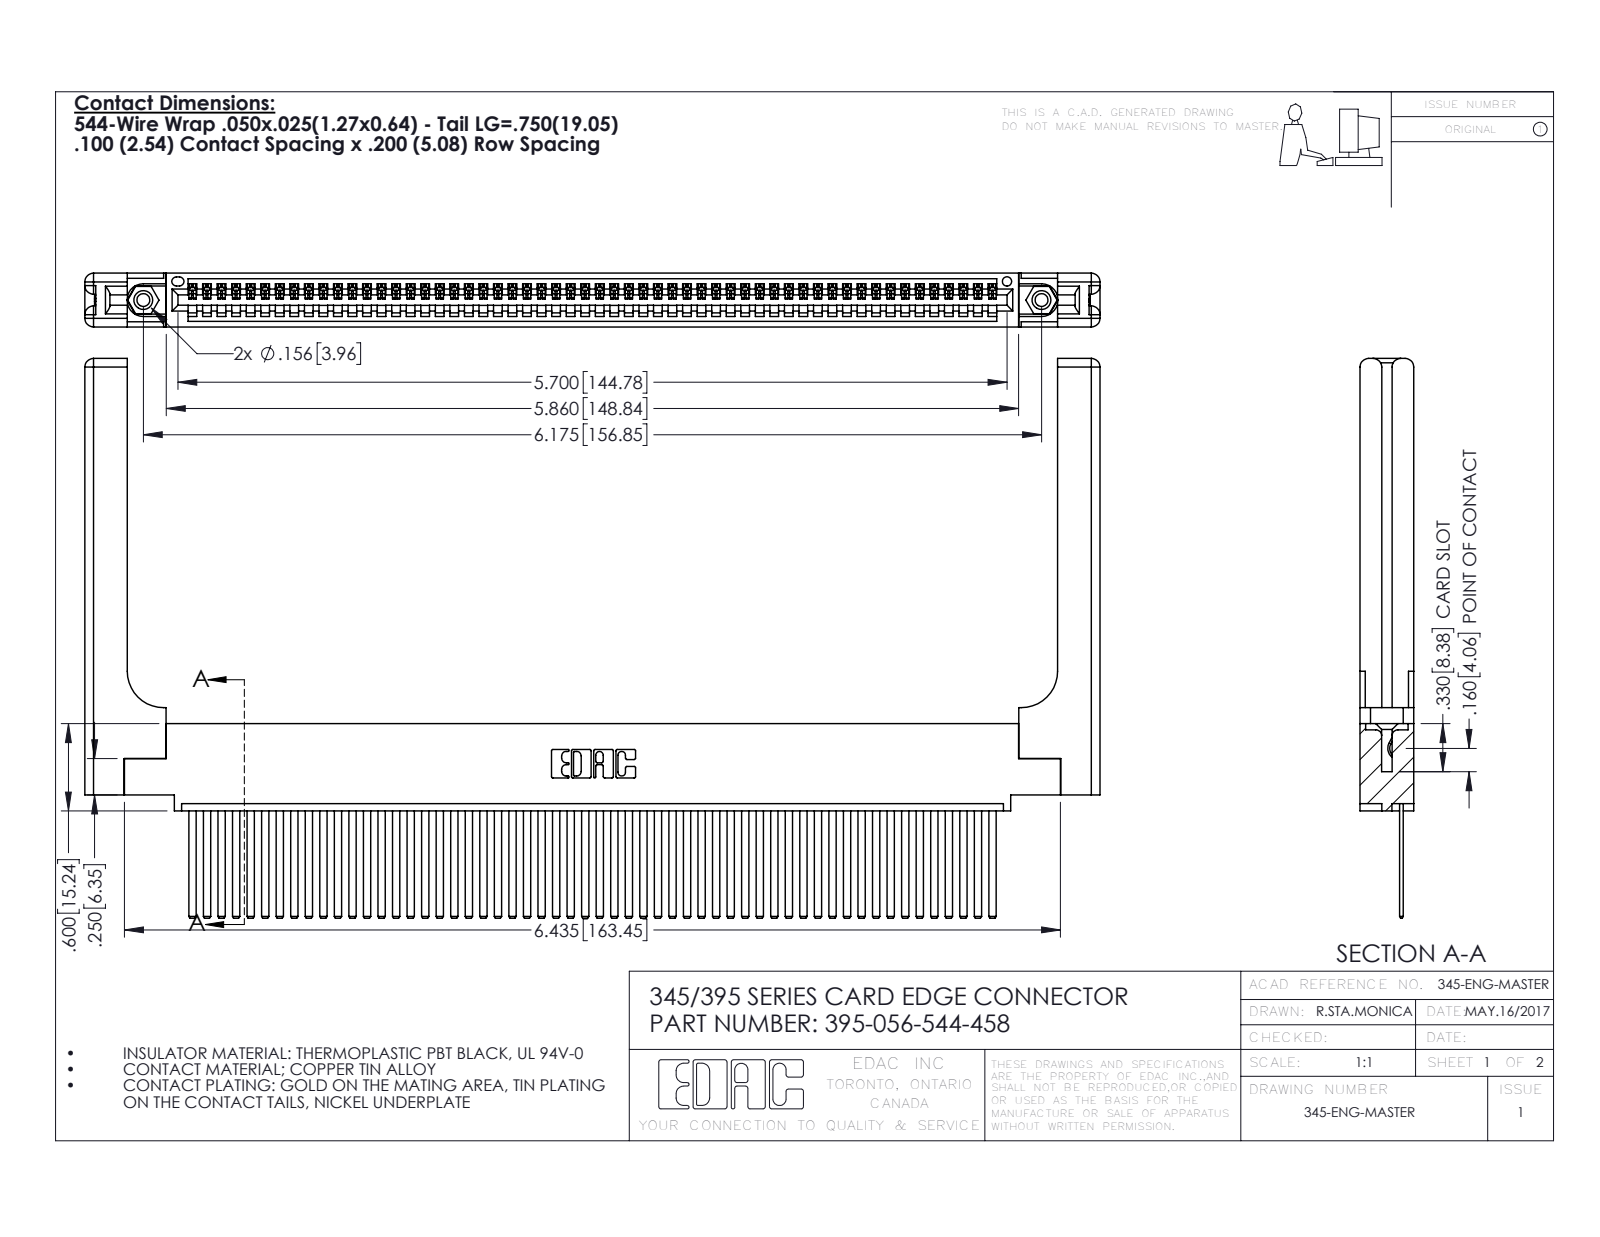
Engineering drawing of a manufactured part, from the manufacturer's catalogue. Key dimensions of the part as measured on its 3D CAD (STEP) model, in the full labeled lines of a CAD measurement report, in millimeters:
Part name (STEP PRODUCT): 345-292-001_345-293-144; 345 Part_0.110 Offset - 0.156 Dia-TH; 345-220-058_345-220-058; 395-056-544-458 (+1 more)
STEP written by: SolidWorks 2016 (CONFIG_CONTROL_DESIGN)
Units: millimetres
Bodies: 61 solids, 3298 faces (2248 planar, 990 cylindrical, 60 other)
Overall size (bounding box): 177.3 × 97.7 × 9.4
Volume: 26 040 mm³ · Surface area: 30 820 mm²
Round holes (diameter × count): ⌀2.3 ×2, ⌀3.2 ×2, ⌀4 ×2, ⌀1.6 ×1
Round bosses / shafts (diameter × count): ⌀3.9 ×2
Partial cylindrical surfaces — rounded edges, fillets, slot ends (radius × count): R0.2 ×112, R0.3 ×22, R1.5 ×16, R0.2 ×6, R0.8 ×6, R0.7 ×3, R0.8 ×2, R0.8 ×2
Main face-to-face distances: 1.8, 7.6, 9.4, 2.5, 6.9, 0.6, 5.1, 5.7, 3.8, 3.8
Hole centre spacings: 6.9, 150.9, 156.8
